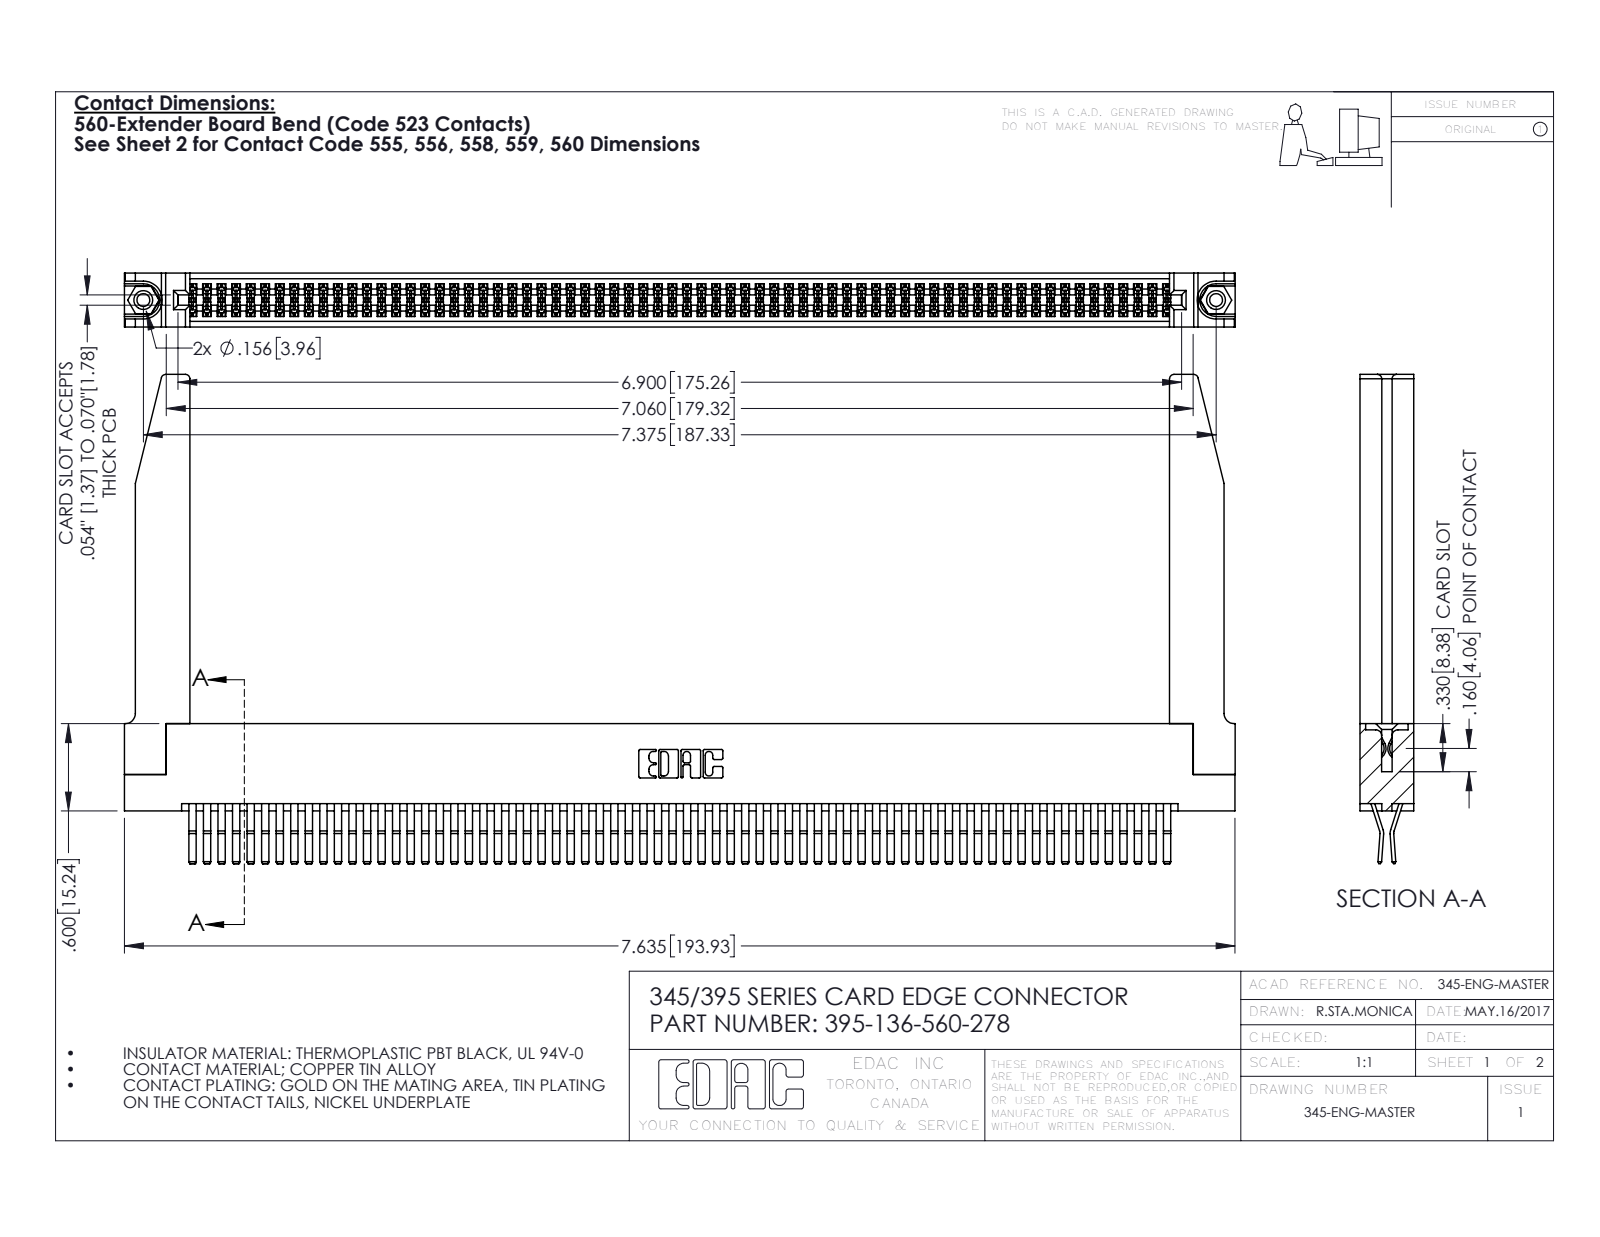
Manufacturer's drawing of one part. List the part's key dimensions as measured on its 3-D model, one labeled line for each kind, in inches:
Part name (STEP PRODUCT): 345-220-078_345-220-078; 395-136-560-278; 345-292-001_560 Tail; 345 Part_Flush Mounting Lugs - 0.156 Dia-TH (+1 more)
STEP written by: SolidWorks 2016 (CONFIG_CONTROL_DESIGN)
Units: inches
Bodies: 141 solids, 7432 faces (4710 planar, 2670 cylindrical, 52 other)
Overall size (bounding box): 7.636 × 3.362 × 0.37
Volume: 1.693 in³ · Surface area: 60.7 in²
Round holes (diameter × count): ⌀0.089 ×2, ⌀0.125 ×2, ⌀0.156 ×2, ⌀0.064 ×1
Round bosses / shafts (diameter × count): ⌀0.155 ×2
Partial cylindrical surfaces — rounded edges, fillets, slot ends (radius × count): R0.006 ×204, R0.01 ×22, R0.03 ×8, R0.007 ×6, R0.031 ×6, R0.026 ×3, R0.01 ×2, R0.014 ×2
Main face-to-face distances: 0.072, 0.025, 0.298, 0.37, 0.2, 0.098, 0.272, 0.225, 0.175, 0.149
Hole centre spacings: 0.27, 7.139, 7.375
